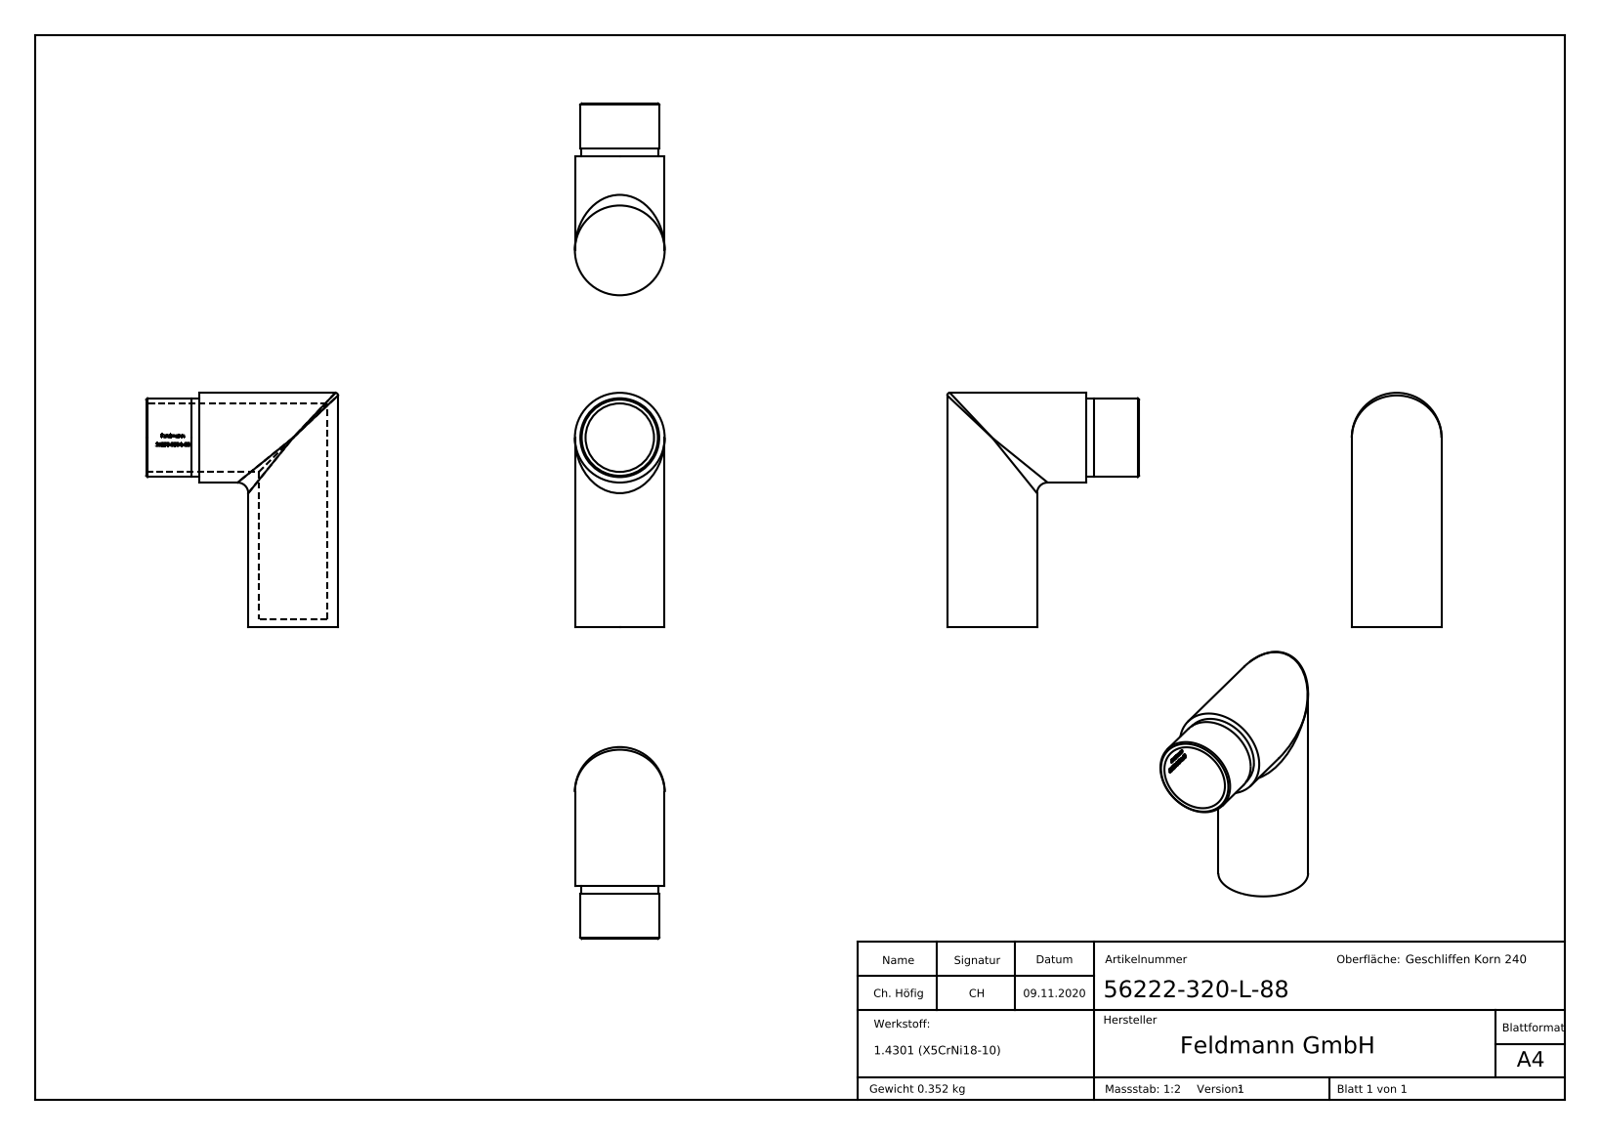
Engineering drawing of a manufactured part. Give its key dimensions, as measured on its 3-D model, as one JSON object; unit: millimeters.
{"part_name": "56222-320-L-88", "step_written_by": "SolidWorks 2018 (CONFIG_CONTROL_DESIGN)", "units": "millimeters", "bodies": {"solids": 1, "faces": 306, "planar": 113, "cylindrical": 43, "other": 150}, "overall_size": [88, 72, 33.7], "volume_mm3": 44617, "surface_area_mm2": 24830, "round_holes": [[25.7, 2]], "round_bosses_or_shafts": [[33.7, 2], [29.6, 1], [29.2, 1]], "partial_cylinders_radius": [[12.95, 1]], "face_to_face_distances": [3, 20, 17, 67.95, 64.95, 0.74, 0.44, 68.08, 65.08, 2.97]}
